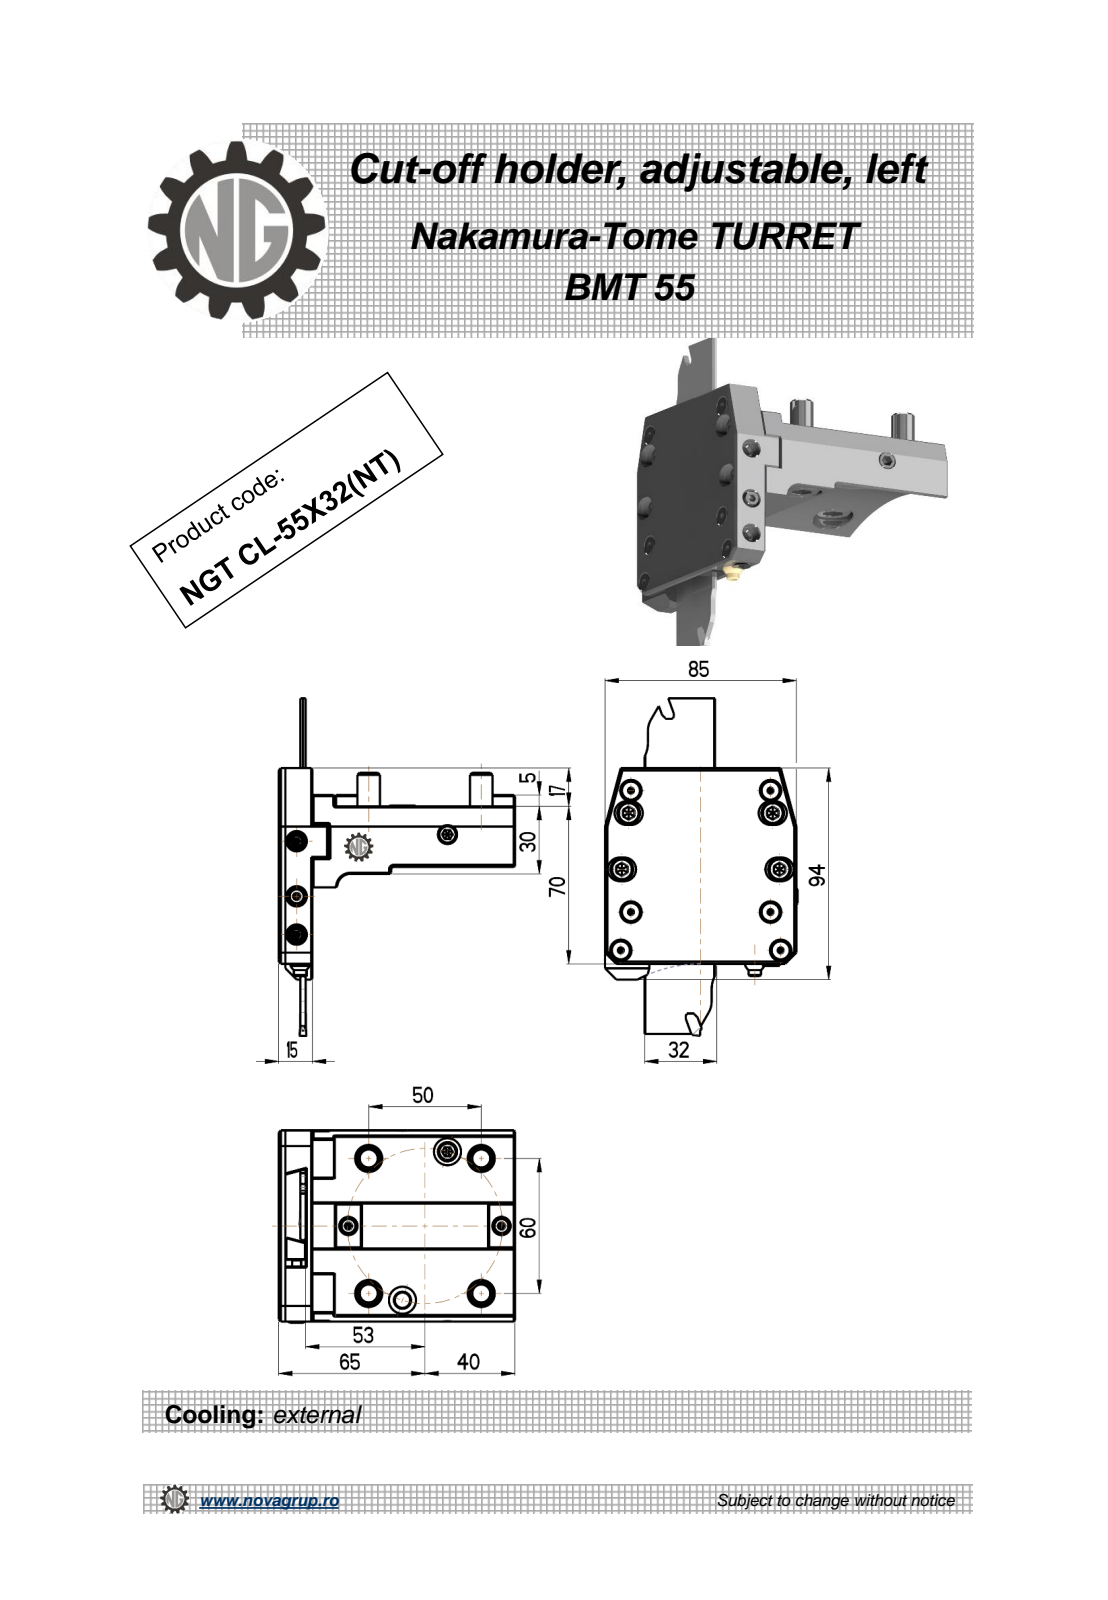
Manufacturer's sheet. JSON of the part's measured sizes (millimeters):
{"part_name": "NGT_CL_55_32_NT", "step_written_by": "PRO/ENGINEER BY PARAMETRIC TECHNOLOGY CORPORATION, 2010280 (CONFIG_CONTROL_DESIGN)", "units": "millimeters", "bodies": {"solids": 1, "faces": 481, "planar": 288, "cylindrical": 116, "other": 77}, "overall_size": [105, 94, 85.53], "volume_mm3": 265640, "surface_area_mm2": 59315, "round_holes": [[5, 2], [8, 2], [12, 2], [3.5, 1], [6.8, 1]], "round_bosses_or_shafts": [[10, 8], [4, 3], [8, 1], [7, 1], [5.5, 1]], "partial_cylinders_radius": [[0.2, 24], [0.31, 12], [5.25, 8], [0.14, 6], [0.16, 6], [0.41, 6], [1, 1], [6, 1]], "face_to_face_distances": [12, 3, 15, 9, 25, 85, 5, 10, 22, 90], "hole_center_spacings": [41.5, 46.38, 68.96, 86.83]}
